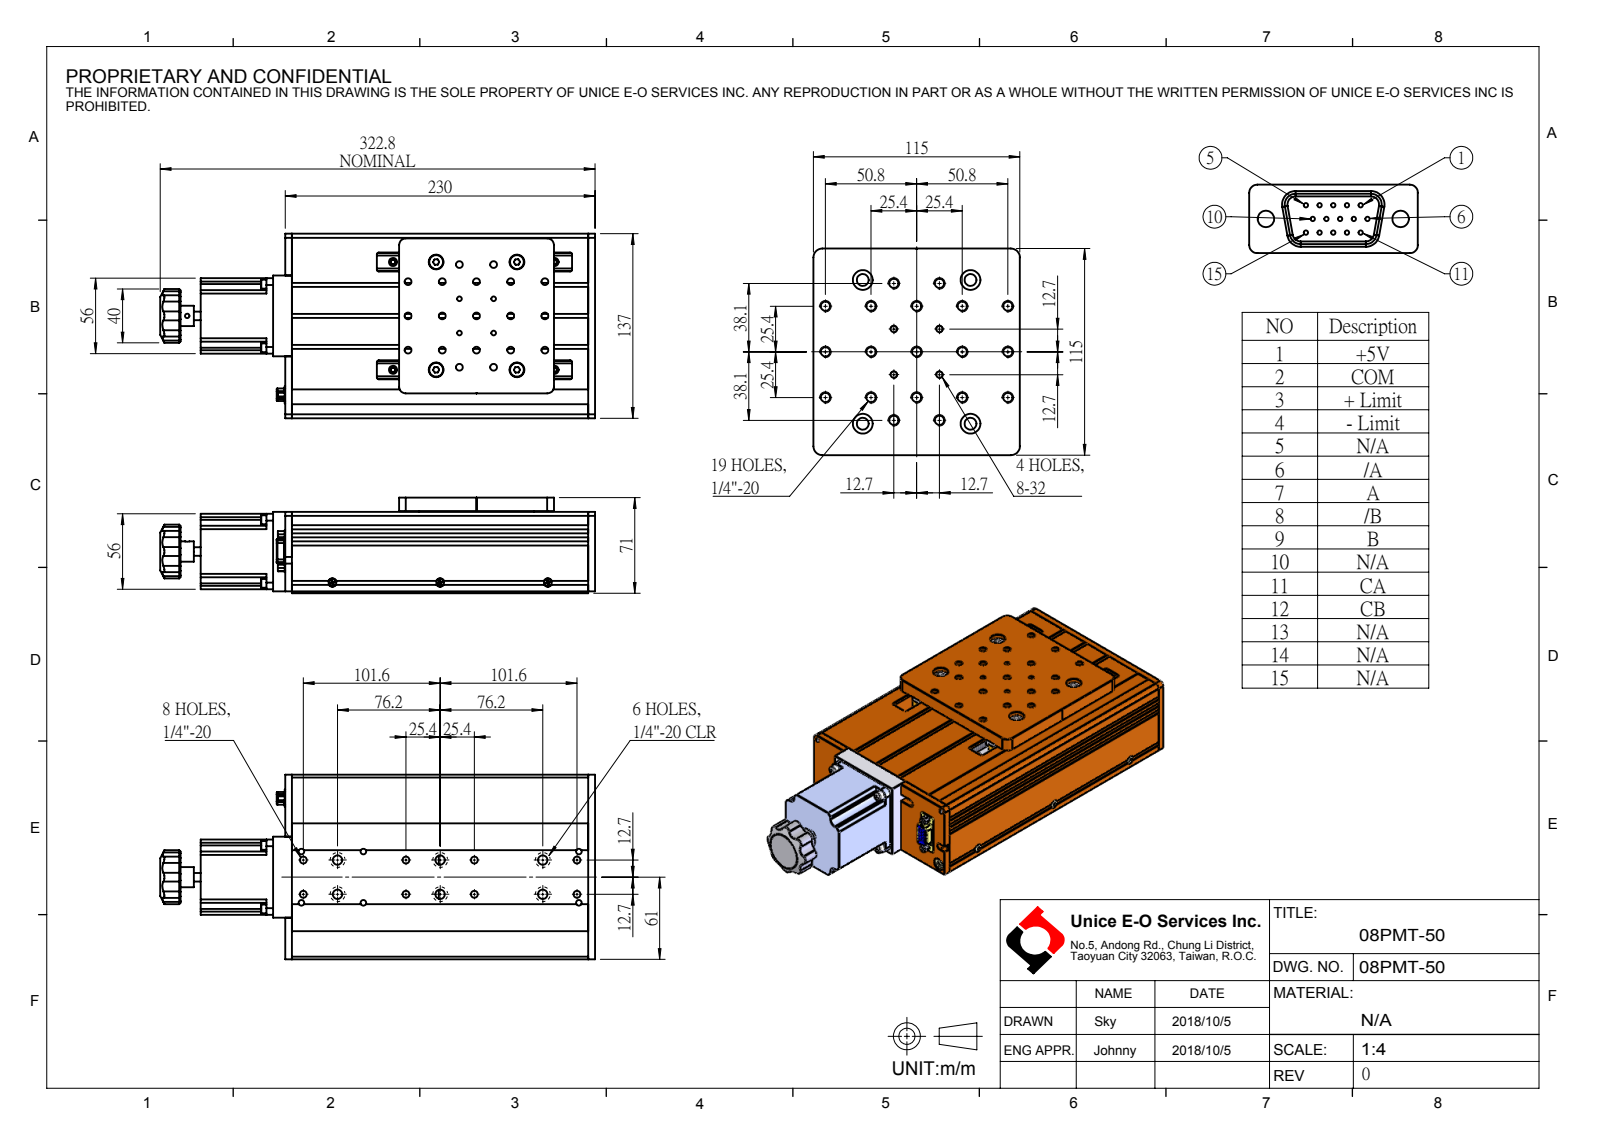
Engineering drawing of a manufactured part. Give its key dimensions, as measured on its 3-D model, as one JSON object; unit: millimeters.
{"part_name": "08PMT-50", "step_written_by": "SolidWorks 2022 (CONFIG_CONTROL_DESIGN)", "units": "millimeters", "bodies": {"solids": 0, "faces": 618, "planar": 389, "cylindrical": 155, "other": 74}, "overall_size": [322.8, 137, 71], "round_holes": [[5.11, 27], [0.8, 15], [11, 10], [4.2, 6], [7, 6], [3.45, 4], [2, 2], [2.5, 2], [3.3, 2]], "round_bosses_or_shafts": [[6.5, 4], [5.8, 3], [7.7, 2], [16, 1], [15, 1], [6.35, 1]], "partial_cylinders_radius": [[1.5, 12], [0.5, 8], [4, 8], [5, 8], [7.41, 8], [2, 4], [4.5, 4], [3, 3]], "face_to_face_distances": [2, 60.5, 135, 1.5, 10.5, 133, 59, 71, 5, 225], "hole_center_spacings": [40.16, 25.4, 17.96, 56.8, 35.92, 64.76, 2.84, 50.8]}
